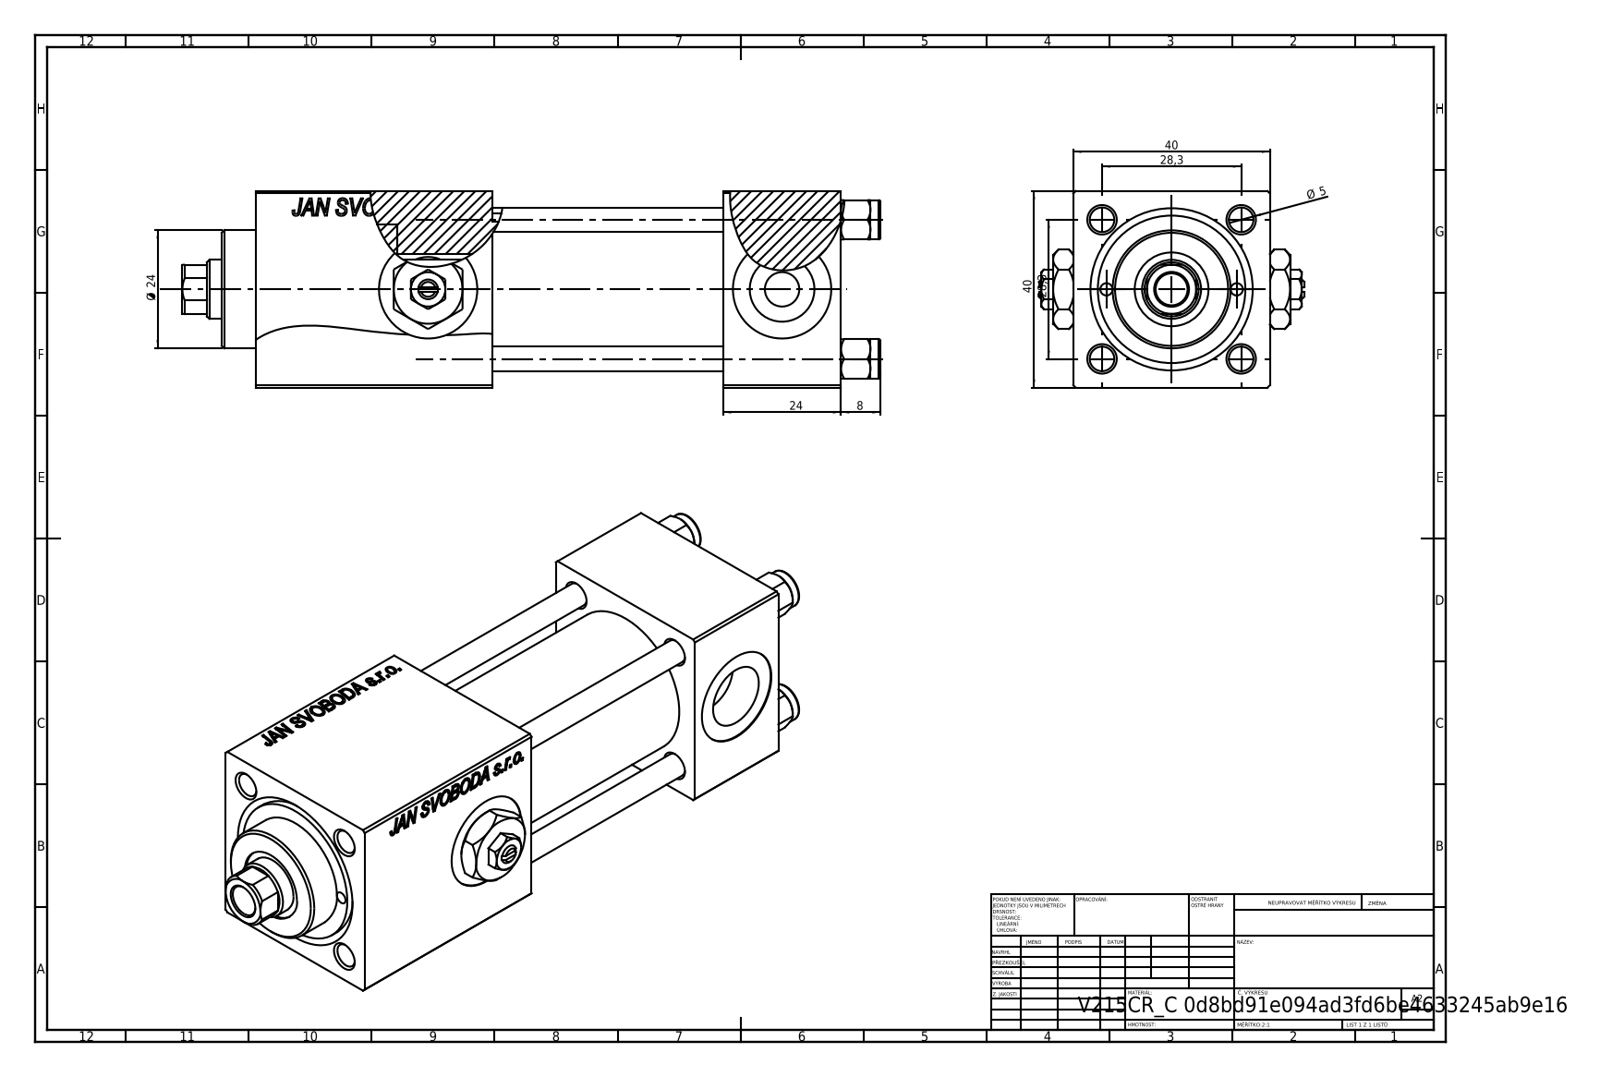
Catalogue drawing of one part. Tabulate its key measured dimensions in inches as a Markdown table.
| quantity | value |
| --- | --- |
| part name | NUT_M5_C; Zatka_pro_OIL_PORT; V215CR_C_Body; V215CR_C_TYCINKA (+2 more) |
| STEP written by | SolidWorks 2019 (CONFIG_CONTROL_DESIGN) |
| units | inches |
| bodies | 13 solids, 1254 faces (574 planar, 102 cylindrical, 578 other) |
| overall size | 5.591 × 2.126 × 1.575 |
| volume | 8.6 in³ |
| surface area | 87.25 in² |
| round holes (diameter × count) | 0.197 × 4, 0.787 × 3, 0.098 × 2, 0.276 × 2, 0.518 × 2, 0.256 × 1, 0.472 × 1, 0.591 × 1, 0.984 × 1, 1.181 × 1 |
| round bosses / shafts (diameter × count) | 0.315 × 4, 1.22 × 1, 0.945 × 1 |
| partial cylindrical surfaces (radius × count) | 0.217 × 1 |
| main face-to-face distances | 1.575, 0.945, 1.567, 3.555, 2.61, 1.85, 1.89, 2.795, 0.76, 3.74 |
| hole center spacings | 0.558, 0.788, 1.114, 1.214, 0.522, 1.576, 1.043, 2.835 |
